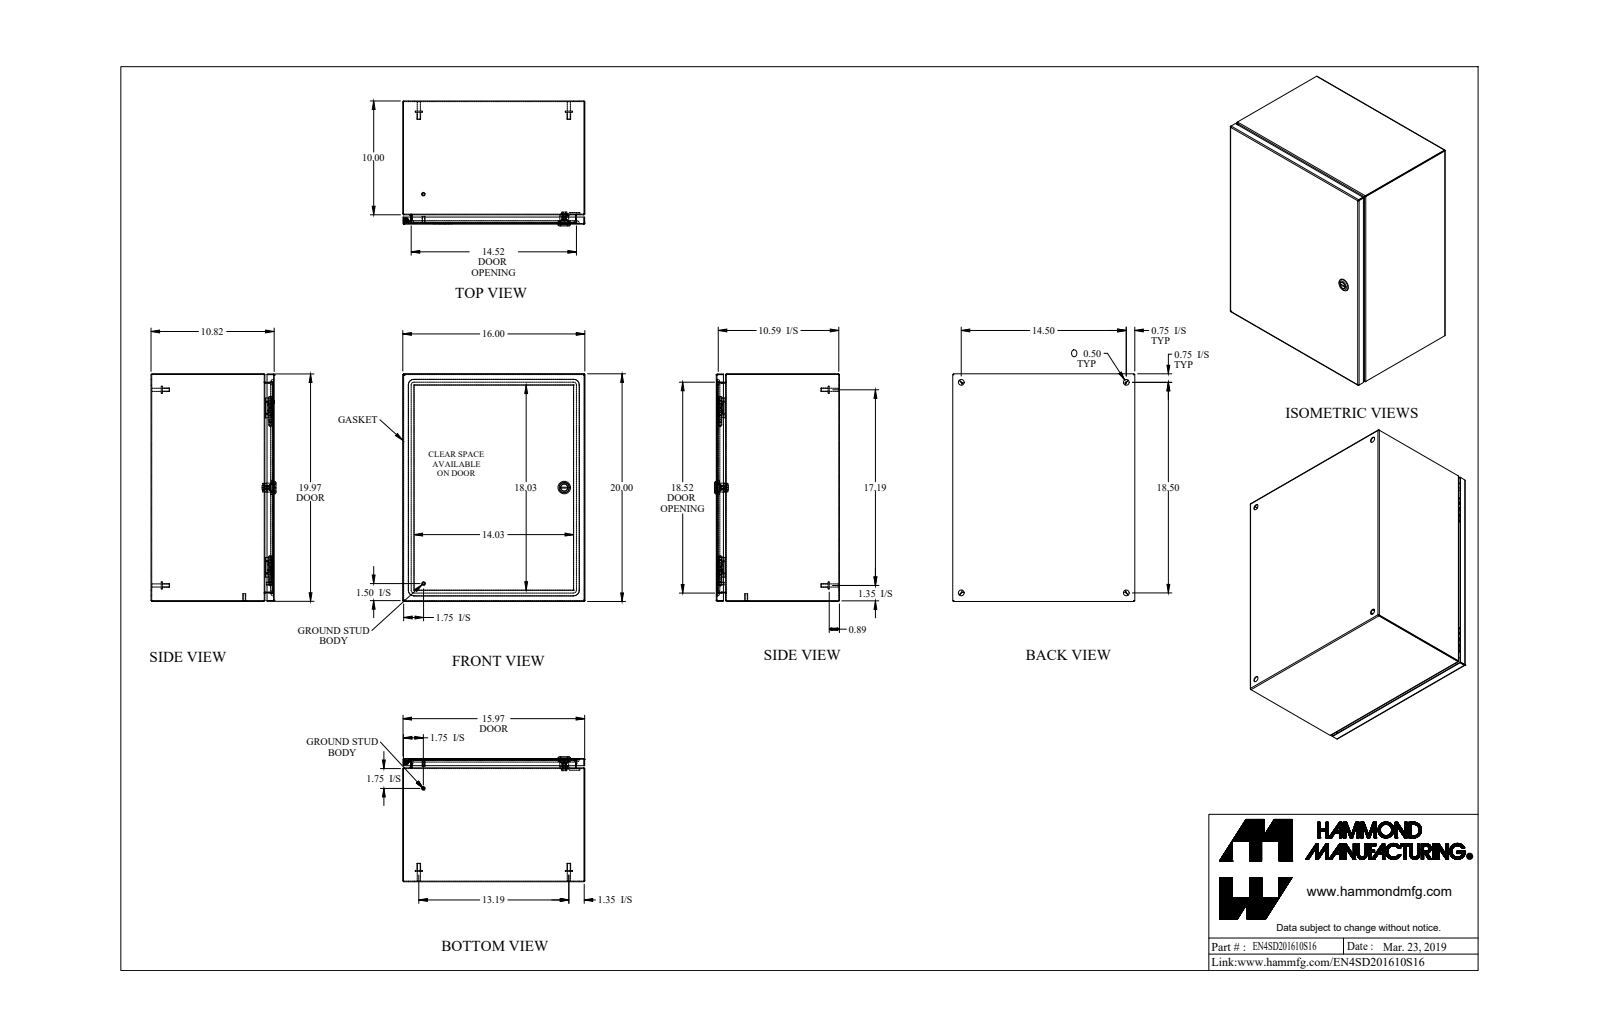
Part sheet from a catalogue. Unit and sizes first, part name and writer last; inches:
Units: inches
Overall size (bounding box): 20 × 16 × 10.981
Round holes (diameter × count): ⌀0.5 ×5, ⌀0.172 ×1, ⌀0.197 ×1, ⌀0.24 ×1, ⌀0.242 ×1, ⌀0.387 ×1, ⌀0.63 ×1, ⌀0.768 ×1
Round bosses / shafts (diameter × count): ⌀0.313 ×6, ⌀0.625 ×4, ⌀0.275 ×4, ⌀0.25 ×2, ⌀1.1 ×1, ⌀0.785 ×1, ⌀0.625 ×1, ⌀0.525 ×1
Partial cylindrical surfaces — rounded edges, fillets, slot ends (radius × count): R0.029 ×21, R0.086 ×21, R0.188 ×12, R0.006 ×4, R0.062 ×4, R0.25 ×4, R0.499 ×4, R0.125 ×2
Main face-to-face distances: 0.057, 15.943, 0.057, 10.707, 10.764, 10.764, 10.821, 19.943, 15.886, 16
Hole centre spacings: 9.31, 14.5, 16.316, 18.5, 23.506
Volume: 92.62 in³ · Surface area: 3 163 in²
Bodies: 22 solids, 656 faces (303 planar, 211 cylindrical, 142 other)
Part name (STEP PRODUCT): EN4SD201610S16_Default
STEP written by: SolidWorks 2019 (CONFIG_CONTROL_DESIGN)
